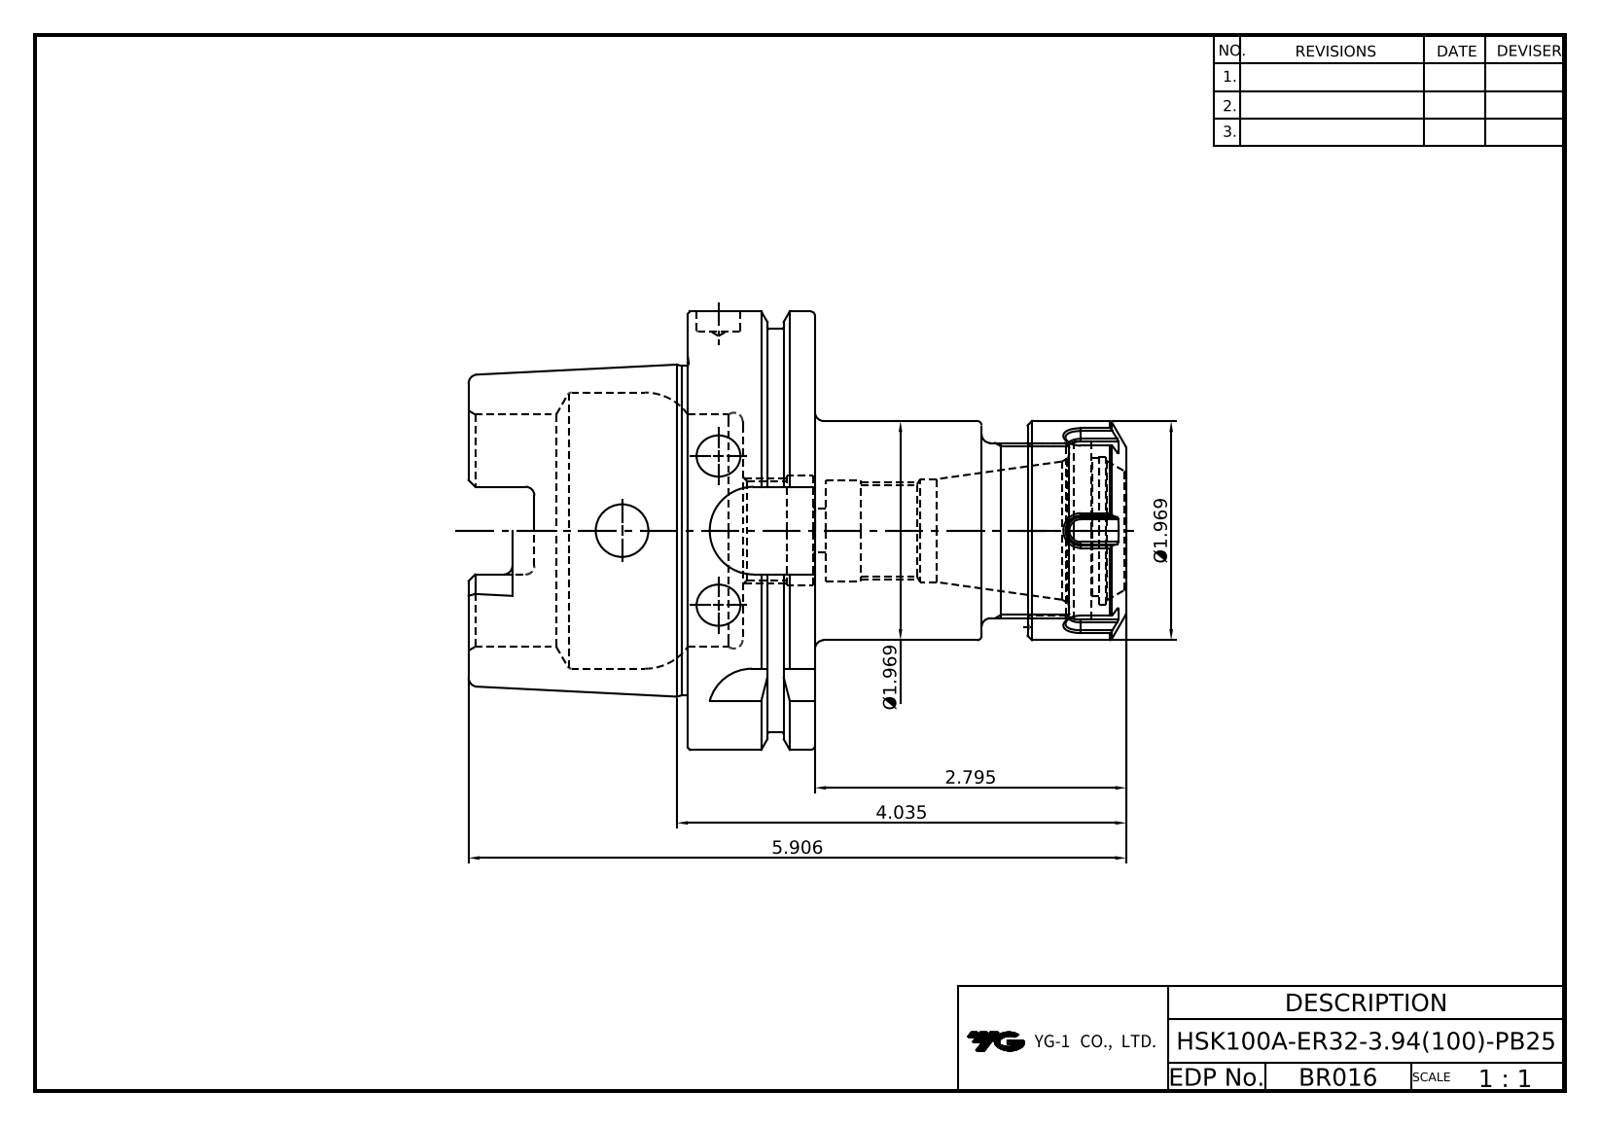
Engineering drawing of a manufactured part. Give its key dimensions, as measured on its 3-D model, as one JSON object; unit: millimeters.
{"part_name": "HSK100A-ER32-3.94; ER32NUT", "step_written_by": "Autodesk Inventor 2020 (AUTOMOTIVE_DESIGN)", "units": "millimeters", "bodies": {"solids": 2, "faces": 206, "planar": 76, "cylindrical": 56, "other": 74}, "overall_size": [150, 100, 100], "volume_mm3": 344099, "surface_area_mm2": 72126, "round_holes": [[10, 2], [1, 1], [12, 1], [20.5, 1], [22.38, 1], [23, 1], [23.5, 1], [25, 1], [27.1, 1], [31.4, 1], [33.8, 1], [38.6, 1]], "round_bosses_or_shafts": [[100, 1], [92, 1], [75.41, 1], [50, 1], [40, 1]], "partial_cylinders_radius": [[0.5, 12], [2, 6], [4.88, 4], [10, 4]], "face_to_face_distances": [29, 12.5, 16.5, 62.5, 50, 79, 22.5, 77.5, 71.5, 150], "hole_center_spacings": [0.8, 22.01, 22.81]}
